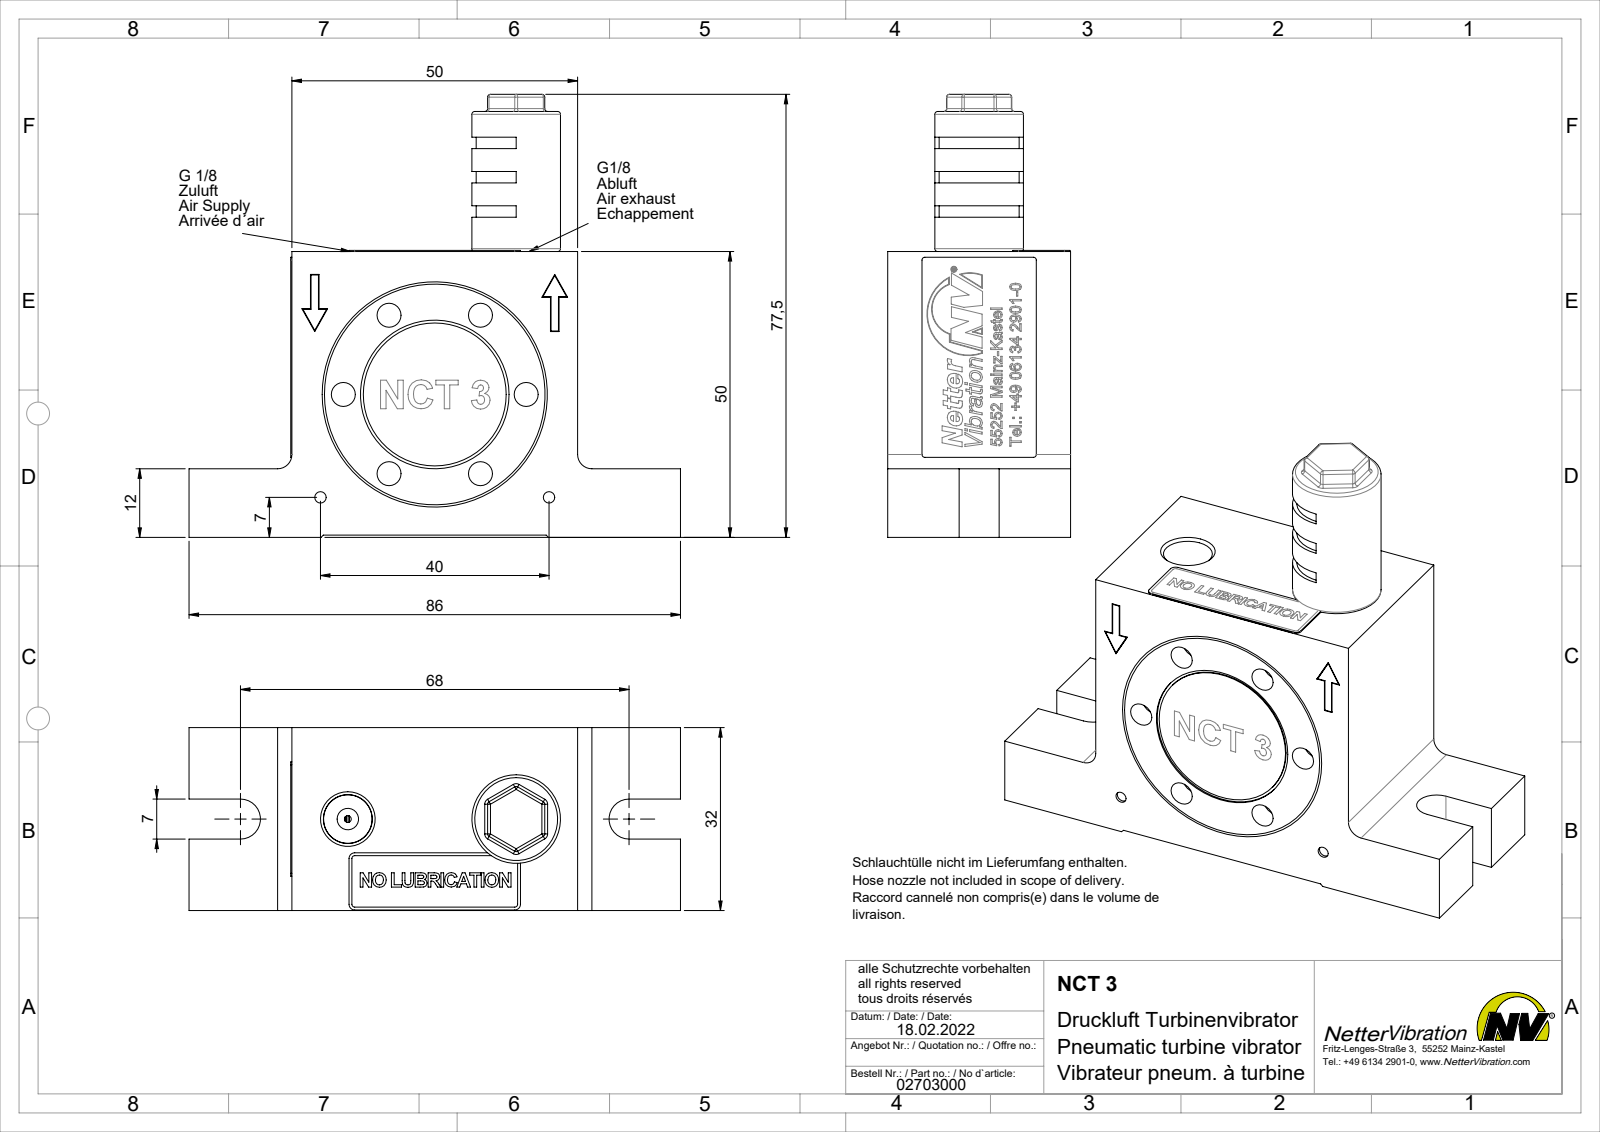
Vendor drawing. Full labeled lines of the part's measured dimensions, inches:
Part name (STEP PRODUCT): NCT 3 Turbinenvibrator #02703000
STEP written by: SolidWorks 2015 (AUTOMOTIVE_DESIGN)
Units: inches
Bodies: 6 solids, 340 faces (204 planar, 77 cylindrical, 59 other)
Overall size (bounding box): 3.386 × 3.051 × 1.27
Volume: 5.885 in³ · Surface area: 40.52 in²
Round holes (diameter × count): ⌀0.165 ×6, ⌀0.079 ×2, ⌀0.337 ×2, ⌀0.709 ×1, ⌀1.024 ×1, ⌀1.511 ×1
Round bosses / shafts (diameter × count): ⌀1.575 ×1, ⌀1.475 ×1, ⌀1.389 ×1, ⌀0.984 ×1, ⌀0.61 ×1, ⌀0.383 ×1
Partial cylindrical surfaces — rounded edges, fillets, slot ends (radius × count): R0.02 ×22, R0.039 ×4, R0.098 ×2, R0.138 ×2, R0.276 ×1
Main face-to-face distances: 1.969, 1.26, 0.236, 0.016, 1.953, 0.325, 1.024, 0.089, 0.935, 0.323
Hole centre spacings: 0.63, 1.091, 0.5, 0.726, 1.059, 1.091, 1.114, 1.26
